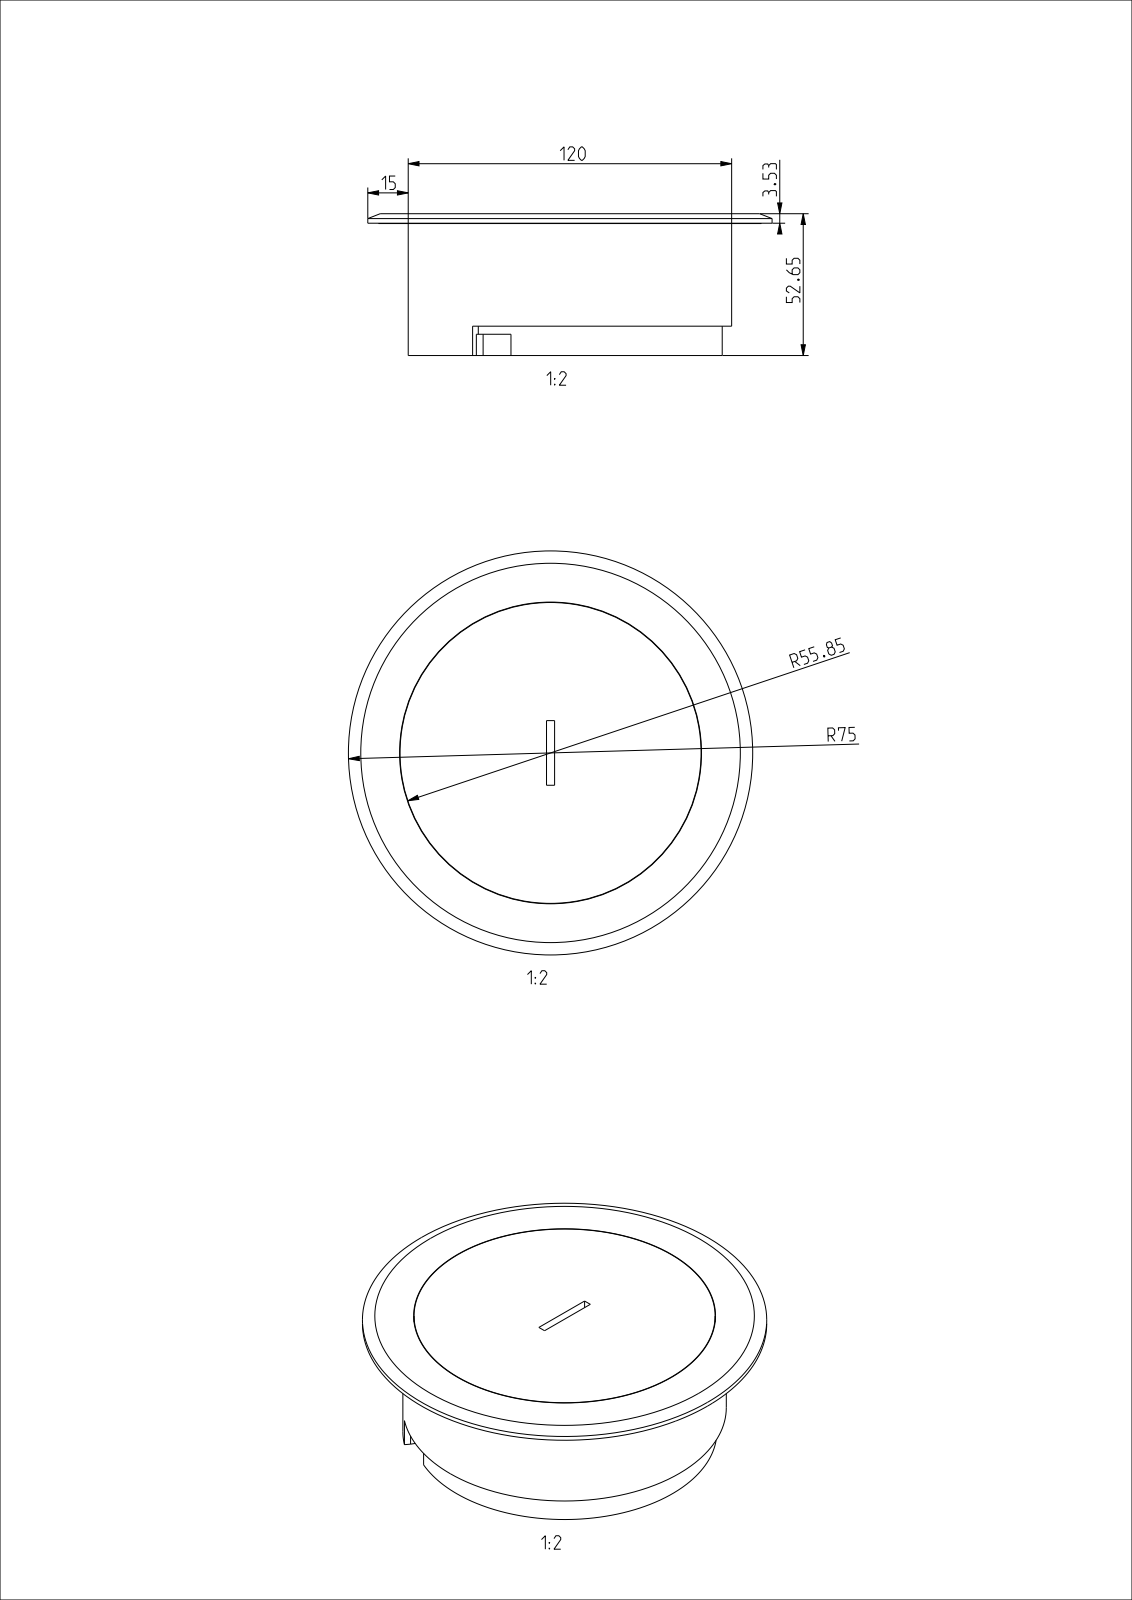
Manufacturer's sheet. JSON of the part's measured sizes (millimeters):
{"part_name": "BSR_BECHEROBERTEIL_6; BSR_DECKEL_TUBUS_3; LAR02MTSKUN_ASM_1_ASM; LAR02MTS_ASM", "step_written_by": "CREO PARAMETRIC BY PTC INC, 2022281 (AUTOMOTIVE_DESIGN)", "units": "millimeters", "bodies": {"solids": 2, "faces": 102, "planar": 76, "cylindrical": 24, "other": 2}, "overall_size": [150, 150, 52.65], "volume_mm3": 171139, "surface_area_mm2": 105043, "round_holes": [[85, 1], [112, 1], [115.4, 1], [145.02, 1]], "round_bosses_or_shafts": [[150, 1], [142, 1], [120, 1], [115.64, 1], [111.7, 1]], "partial_cylinders_radius": [[53, 1], [55, 1], [56.5, 1]], "face_to_face_distances": [2.25, 3.75, 6, 2.35, 1.4, 3.65, 6.3, 8.65, 10.05, 12.3]}
